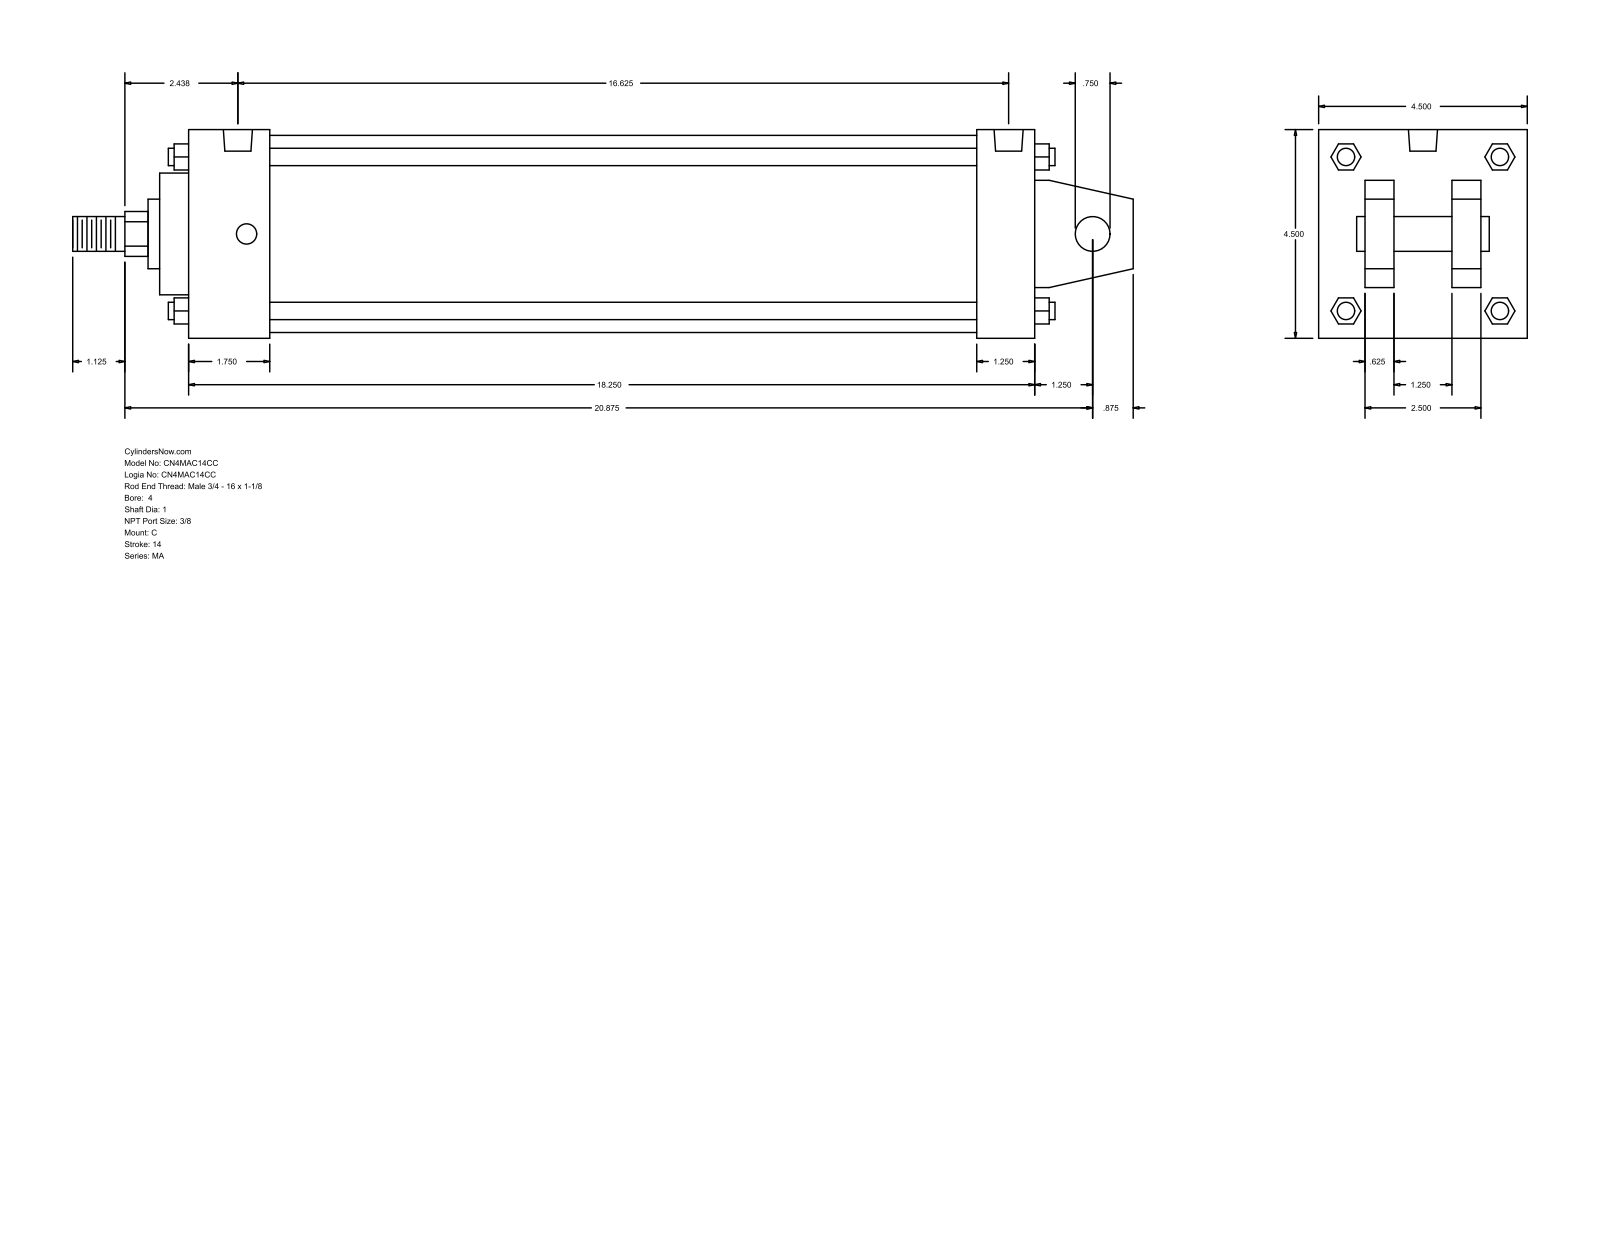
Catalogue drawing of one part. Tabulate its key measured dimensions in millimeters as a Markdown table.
| quantity | value |
| --- | --- |
| part name | MA_C__0400_1 |
| STEP written by | GSSL Pune (CONFIG_CONTROL_DESIGN) |
| units | millimeters |
| bodies | 0 solids, 141 faces (109 planar, 32 cylindrical, 0 other) |
| overall size | 581.02 × 114.3 × 114.3 |
| round holes (diameter × count) | 11.11 × 4, 15.93 × 2 |
| round bosses / shafts (diameter × count) | 9.53 × 4, 19.05 × 2, 107.95 × 1, 66.67 × 1, 38.1 × 1, 25.4 × 1 |
| partial cylindrical surfaces (radius × count) | 12.29 × 1 |
| main face-to-face distances | 114.3, 463.56, 15.87, 73.03, 41.27, 25.4, 88.9, 47.63, 431.81, 31.75 |
| hole center spacings | 4.76, 412.76, 417.52, 422.28 |
